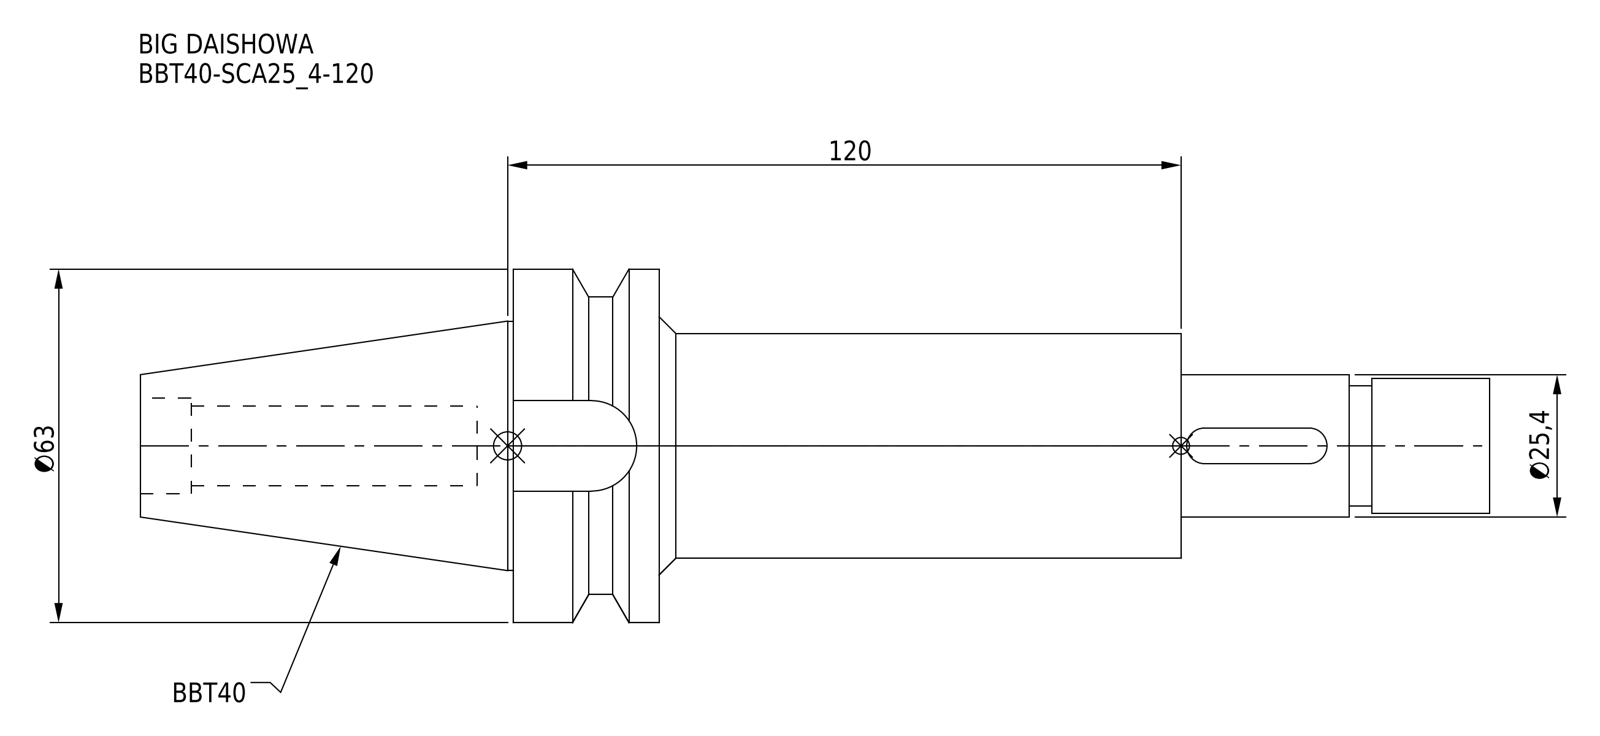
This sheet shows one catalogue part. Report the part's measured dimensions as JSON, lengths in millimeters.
{"part_name": "BBT40-SCA25_4-120", "step_written_by": "CREO PARAMETRIC BY PTC INC, 2016380 (AUTOMOTIVE_DESIGN)", "units": "millimeters", "bodies": {"solids": 1, "faces": 50, "planar": 18, "cylindrical": 24, "other": 8}, "overall_size": [240.4, 63, 63], "volume_mm3": 269439, "surface_area_mm2": 37621, "round_holes": [[14.2, 1], [17, 1]], "round_bosses_or_shafts": [[63, 1], [53, 1], [44.45, 1], [40, 1], [25.4, 1], [24, 1], [21.5, 1]], "partial_cylinders_radius": [[3.17, 2], [8.05, 1]], "face_to_face_distances": [26, 93, 119, 55, 148, 174, 45, 240.4, 185.4, 92.4]}
